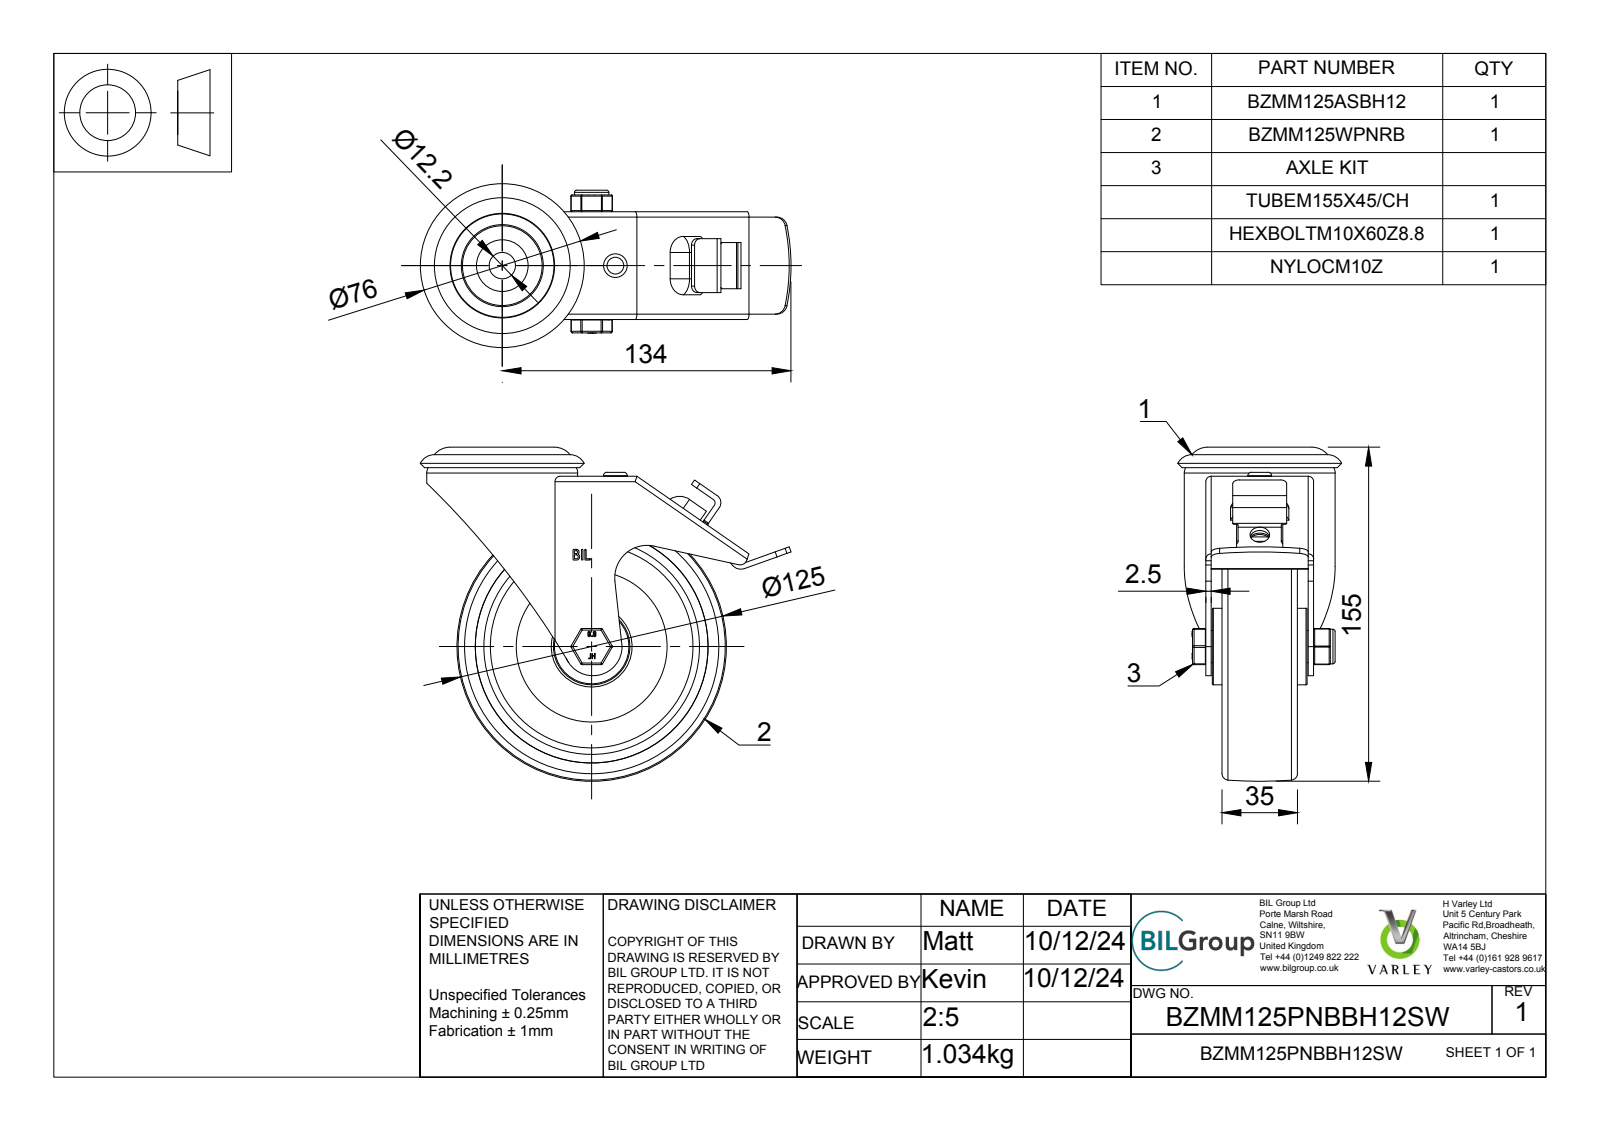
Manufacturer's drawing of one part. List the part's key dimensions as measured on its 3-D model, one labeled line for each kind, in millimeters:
Part name (STEP PRODUCT): BZMM125PNBBH12SW v6; BZMM125WPNRB v1; POLYURETHANE TYRE; NYLON RIM (+7 more)
STEP written by: Autodesk Translation Framework v13.20.0.188 (AP242_MANAGED_MODEL_BASED_3D_ENGINEERING_MIM_LF)
Units: millimetres
Bodies: 22 solids, 736 faces (370 planar, 253 cylindrical, 113 other)
Overall size (bounding box): 172 × 155 × 76
Volume: 322 208 mm³ · Surface area: 167 388 mm²
Round holes (diameter × count): ⌀6 ×2, ⌀9 ×1, ⌀10 ×1, ⌀10.2 ×1, ⌀12 ×1, ⌀12.2 ×1, ⌀15.5 ×1, ⌀16 ×1, ⌀23.5 ×1, ⌀26 ×1, ⌀65 ×1, ⌀72 ×1
Round bosses / shafts (diameter × count): ⌀4 ×8, ⌀70 ×1, ⌀49.5 ×1, ⌀38 ×1, ⌀35.5 ×1, ⌀25.9 ×1, ⌀24 ×1, ⌀22.75 ×1
Partial cylindrical surfaces — rounded edges, fillets, slot ends (radius × count): R0.75 ×60, R0.5 ×32, R1.5 ×7, R1.25 ×6, R3 ×6, R4 ×6, R2.5 ×5, R2 ×3
Main face-to-face distances: 2.5, 19.75, 47.5, 5, 20.25, 40, 7.5, 22.75, 27.25, 24.75
Hole centre spacings: 52.5
